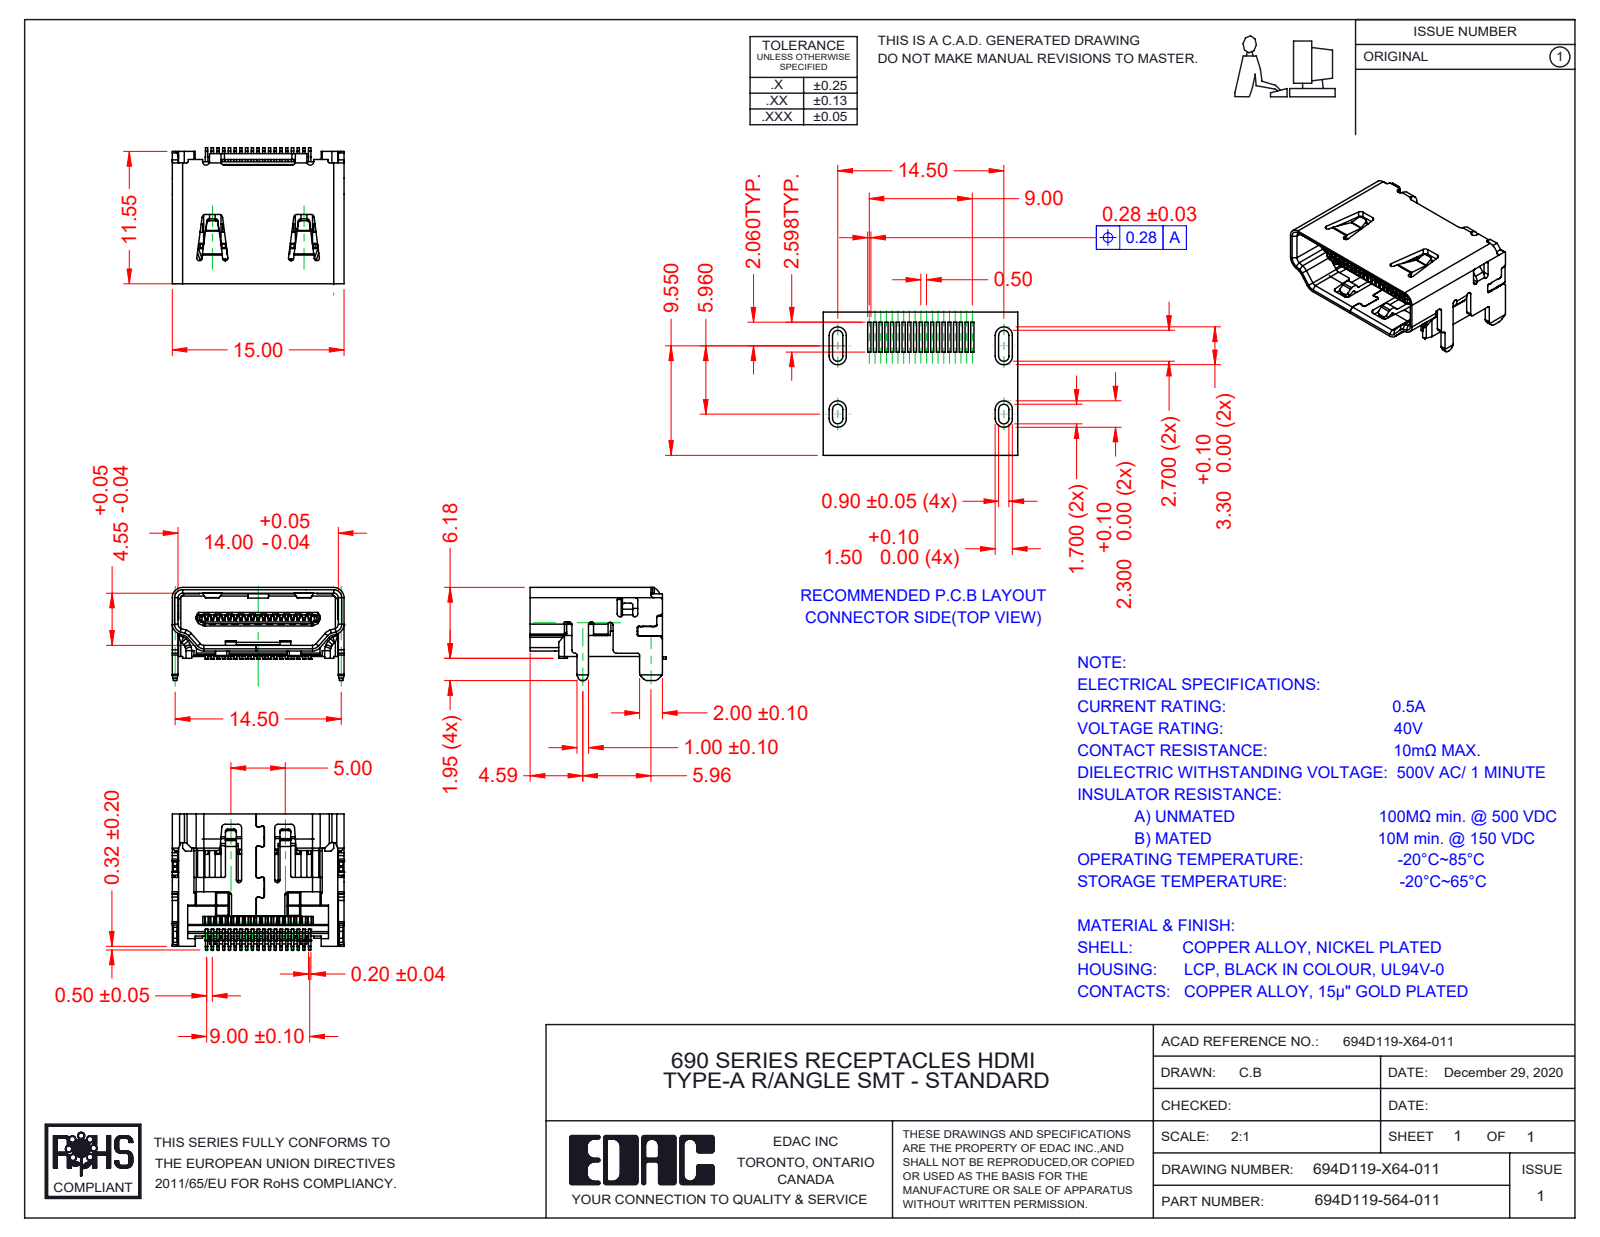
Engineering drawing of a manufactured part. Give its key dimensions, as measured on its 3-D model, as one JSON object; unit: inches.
{"part_name": "694D119-164-011; Shell 694D119-X64-011; Insulator 694D119-X64-011", "step_written_by": "SolidWorks 2020 (AUTOMOTIVE_DESIGN)", "units": "inches", "bodies": {"solids": 2, "faces": 1880, "planar": 1391, "cylindrical": 429, "other": 60}, "overall_size": [0.591, 0.467, 0.32], "volume_in3": 0.028, "surface_area_in2": 2.396, "partial_cylinders_radius": [[0.008, 114], [0.005, 30], [0.012, 21], [0.006, 19], [0.02, 10], [0.007, 8], [0.016, 7], [0.009, 6]], "face_to_face_distances": [0.02, 0.199, 0.028, 0.571, 0.022, 0.112, 0.152, 0.035, 0.072, 0.039]}
